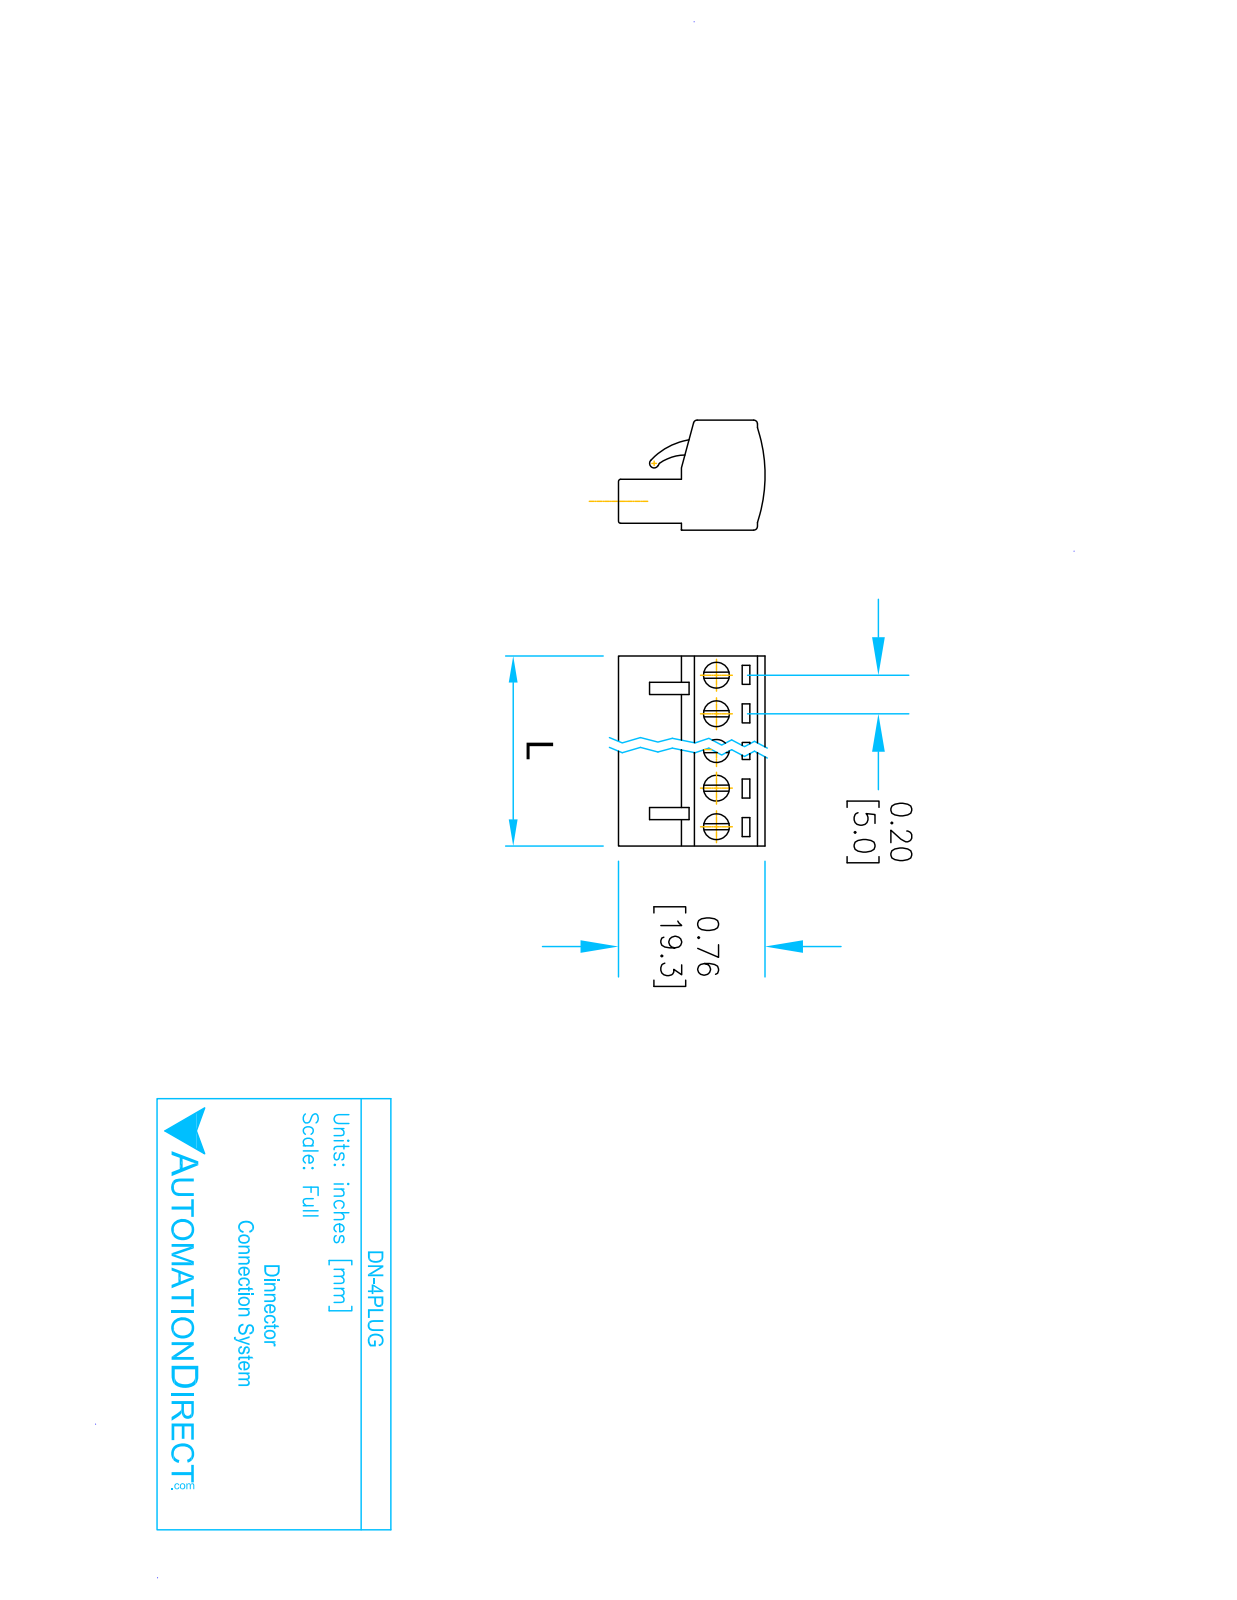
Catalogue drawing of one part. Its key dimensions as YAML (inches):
part_name: "49004_S; 49001_S; 49002_S; 49001_S_49002_SENZA DENTE"
step_written_by: "SolidWorks 2013 (AUTOMOTIVE_DESIGN)"
units: inches
bodies: {solids: 3, faces: 356, planar: 247, cylindrical: 89, other: 20}
overall_size: [0.8, 0.76, 0.571]
volume: 0.213
surface_area: 5.289
round_holes:
  - {diameter: 0.063, count: 4}
  - {diameter: 0.098, count: 4}
  - {diameter: 0.134, count: 4}
  - {diameter: 0.142, count: 4}
round_bosses_or_shafts:
  - {diameter: 0.118, count: 4}
partial_cylinders:
  - {radius: 0.114, count: 4}
  - {radius: 0.02, count: 3}
  - {radius: 0.012, count: 2}
  - {radius: 0.024, count: 1}
  - {radius: 0.236, count: 1}
  - {radius: 0.354, count: 1}
  - {radius: 0.789, count: 1}
face_to_face_distances: [0.2, 0.4, 0.6, 0.8, 0.264, 0.039, 0.571, 0.307, 0.134, 0.531]
hole_center_spacings: [0.2, 0.4, 0.6]
